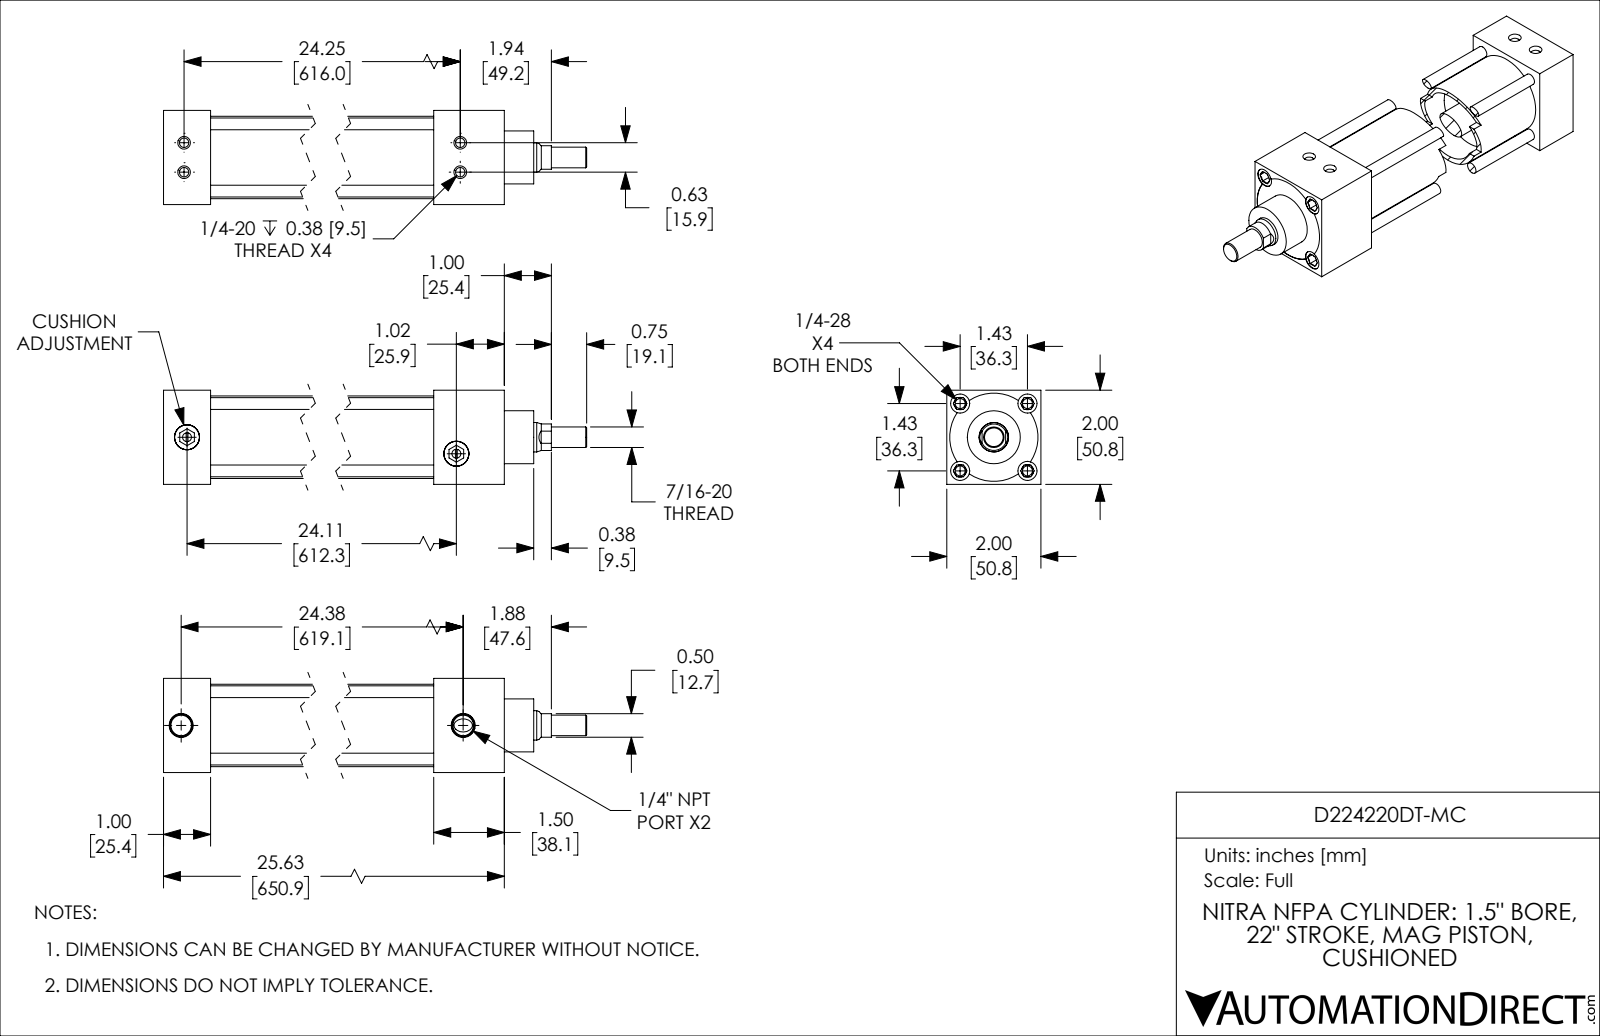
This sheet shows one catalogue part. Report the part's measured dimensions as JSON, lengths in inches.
{"part_name": "D224220DT-MC_BODY; D224220DT-MC_PISTON_KK1; D224220DT-MC_CUSHION; D224220DT-MC", "step_written_by": "SolidWorks 2019 (CONFIG_CONTROL_DESIGN)", "units": "inches", "bodies": {"solids": 4, "faces": 251, "planar": 90, "cylindrical": 81, "other": 80}, "overall_size": [27.375, 2, 2], "volume_in3": 38.27, "surface_area_in2": 415.9, "round_holes": [[0.201, 4], [0.213, 4], [0.406, 4], [0.19, 2], [0.438, 2], [0.531, 2], [0.626, 1], [1.501, 1]], "round_bosses_or_shafts": [[0.25, 4], [0.532, 2], [1.751, 1], [1.499, 1], [1.125, 1], [0.624, 1], [0.437, 1]], "partial_cylinders_radius": [[0.281, 1], [0.937, 1]], "face_to_face_distances": [2, 1, 24.125, 23.125, 25.62, 24.62, 1.495, 1.125, 2.125, 22], "hole_center_spacings": [0.319, 1.011, 1.43, 0.625, 2.022, 24.25, 24.258, 24.314]}
